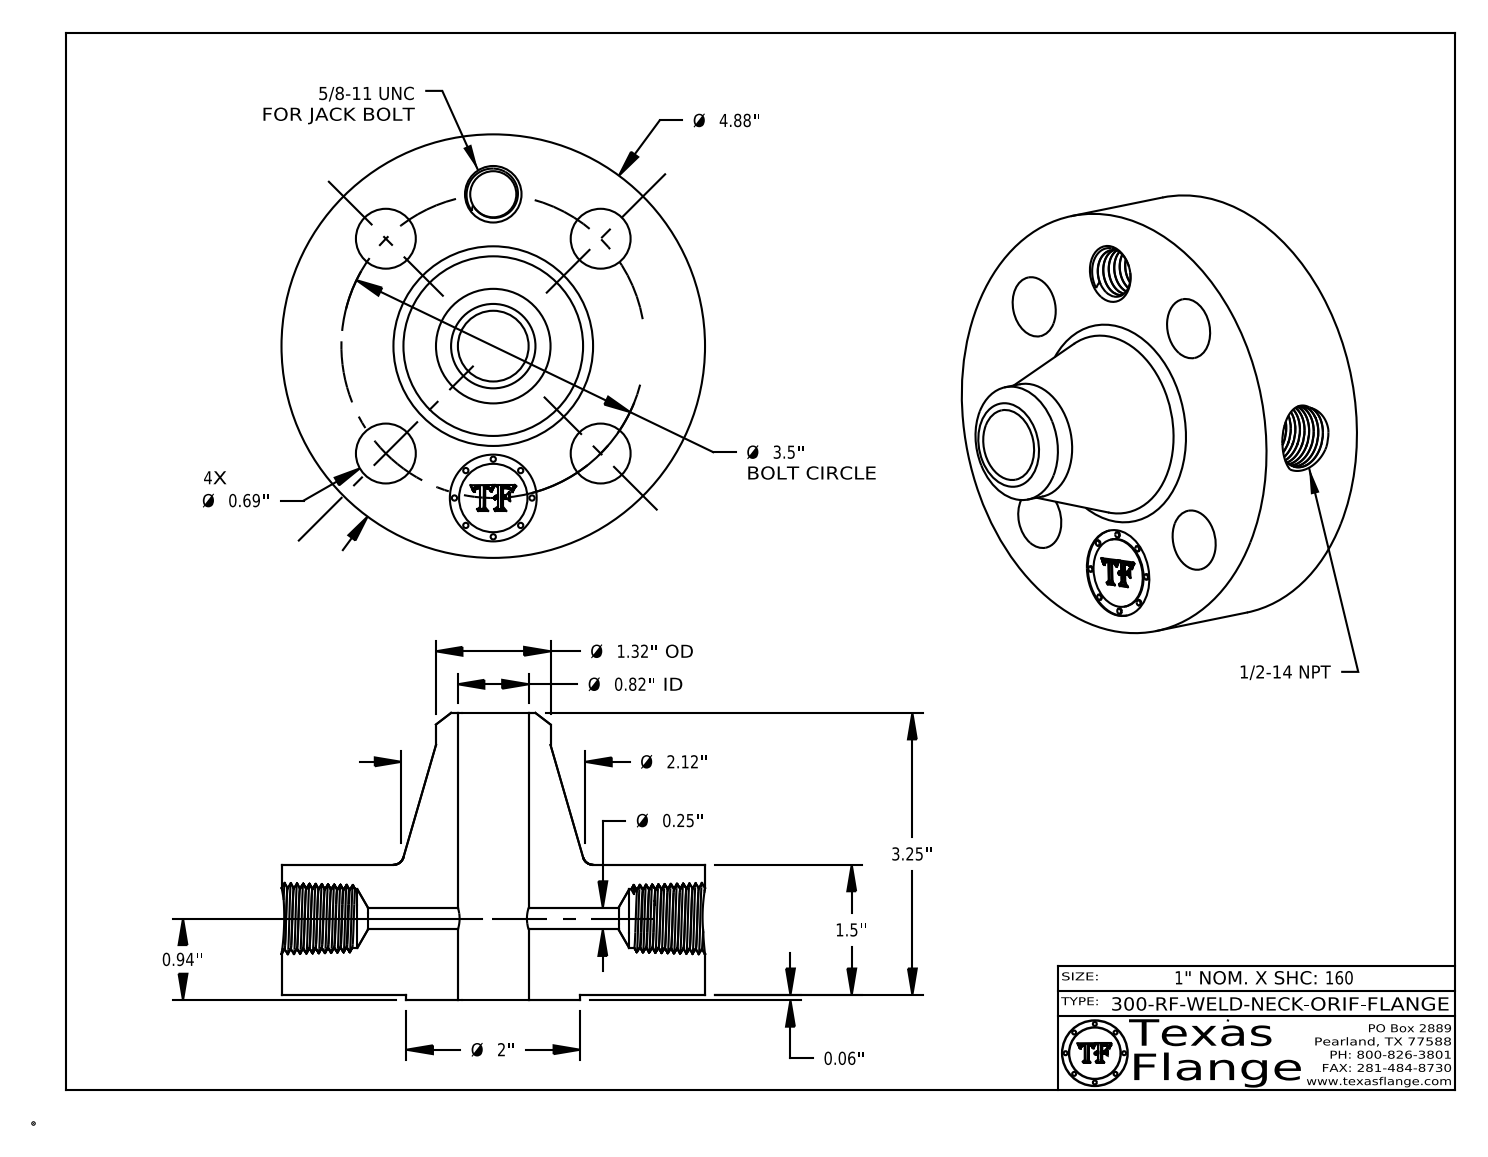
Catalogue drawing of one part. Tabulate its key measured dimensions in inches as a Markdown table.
| quantity | value |
| --- | --- |
| part name | 300-RF-WELD-NECK |
| STEP written by | CATIA V5 STEP AP214 (AUTOMOTIVE_DESIGN) |
| units | inches |
| bodies | 1 solid, 764 faces (369 planar, 87 cylindrical, 308 other) |
| overall size | 4.88 × 4.88 × 3.31 |
| volume | 26.73 in³ |
| surface area | 96.77 in² |
| round holes (diameter × count) | 0.69 × 4, 0.25 × 1, 0.531 × 1, 0.672 × 1, 0.815 × 1, 1 × 1 |
| round bosses / shafts (diameter × count) | 0.061 × 8, 4.88 × 1, 2 × 1, 1.32 × 1, 0.788 × 1 |
| main face-to-face distances | 1.5, 0.06, 1.56, 1.545, 1.485, 0.015, 3.31, 3.25, 1.765, 1.75 |
| hole center spacings | 1.75, 1.339, 2.475, 3.233, 3.5 |
